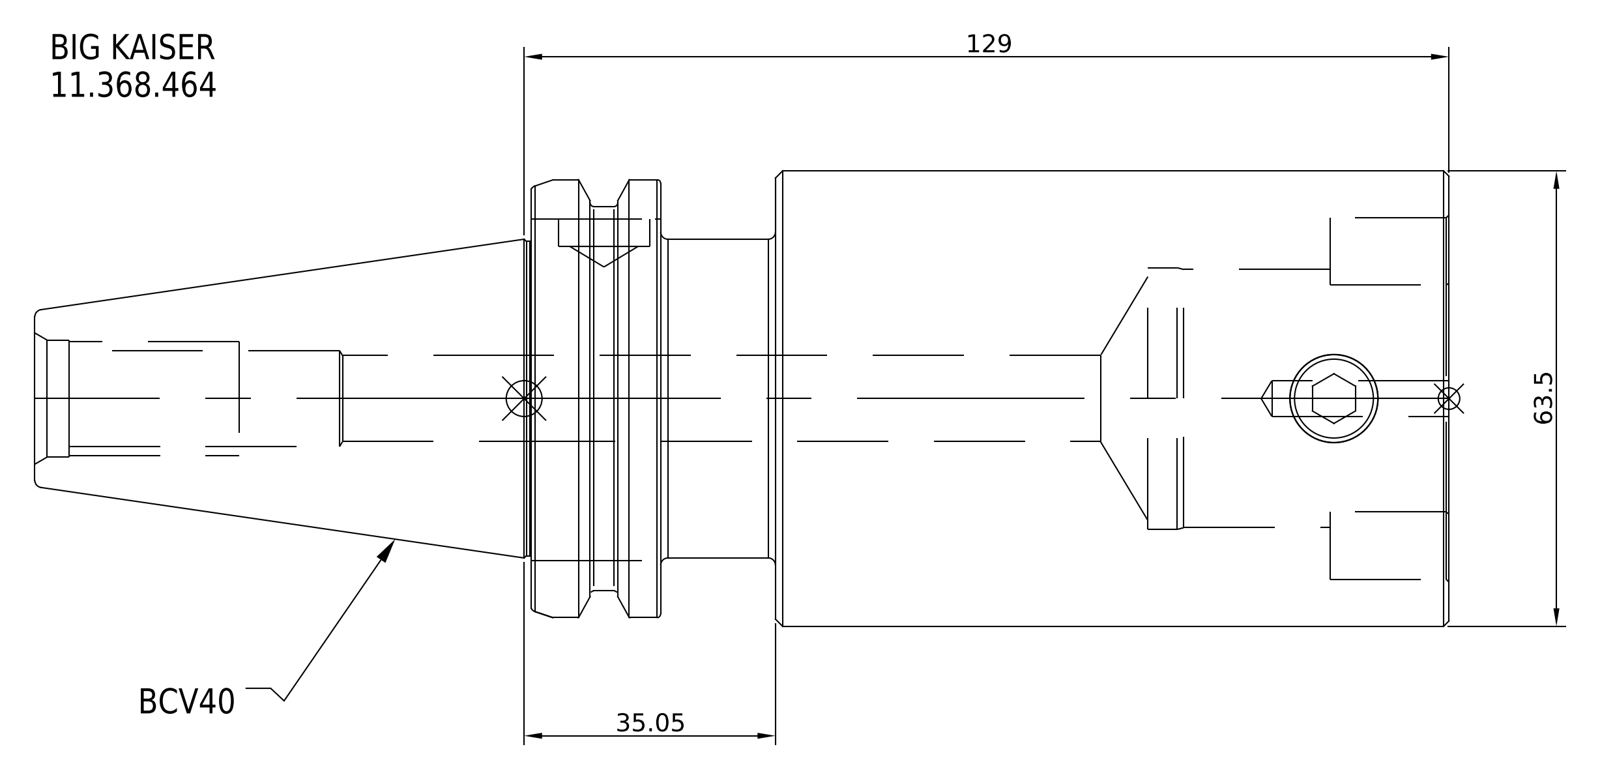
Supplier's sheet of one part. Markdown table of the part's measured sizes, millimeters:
| quantity | value |
| --- | --- |
| part name | 11.368.464 |
| STEP written by | SolidWorks 2021 (CONFIG_CONTROL_DESIGN) |
| units | millimeters |
| bodies | 1 solid, 16 faces (7 planar, 6 cylindrical, 3 other) |
| overall size | 197.25 × 63.5 × 63.5 |
| volume | 439 676 mm³ |
| surface area | 41 330 mm² |
| round bosses / shafts (diameter × count) | 63.5 × 1, 56.36 × 1, 44.45 × 1 |
| main face-to-face distances | 93.95, 125.83, 31.88, 109.95, 16, 15.88, 197.25, 103.3, 87.3, 71.42 |
